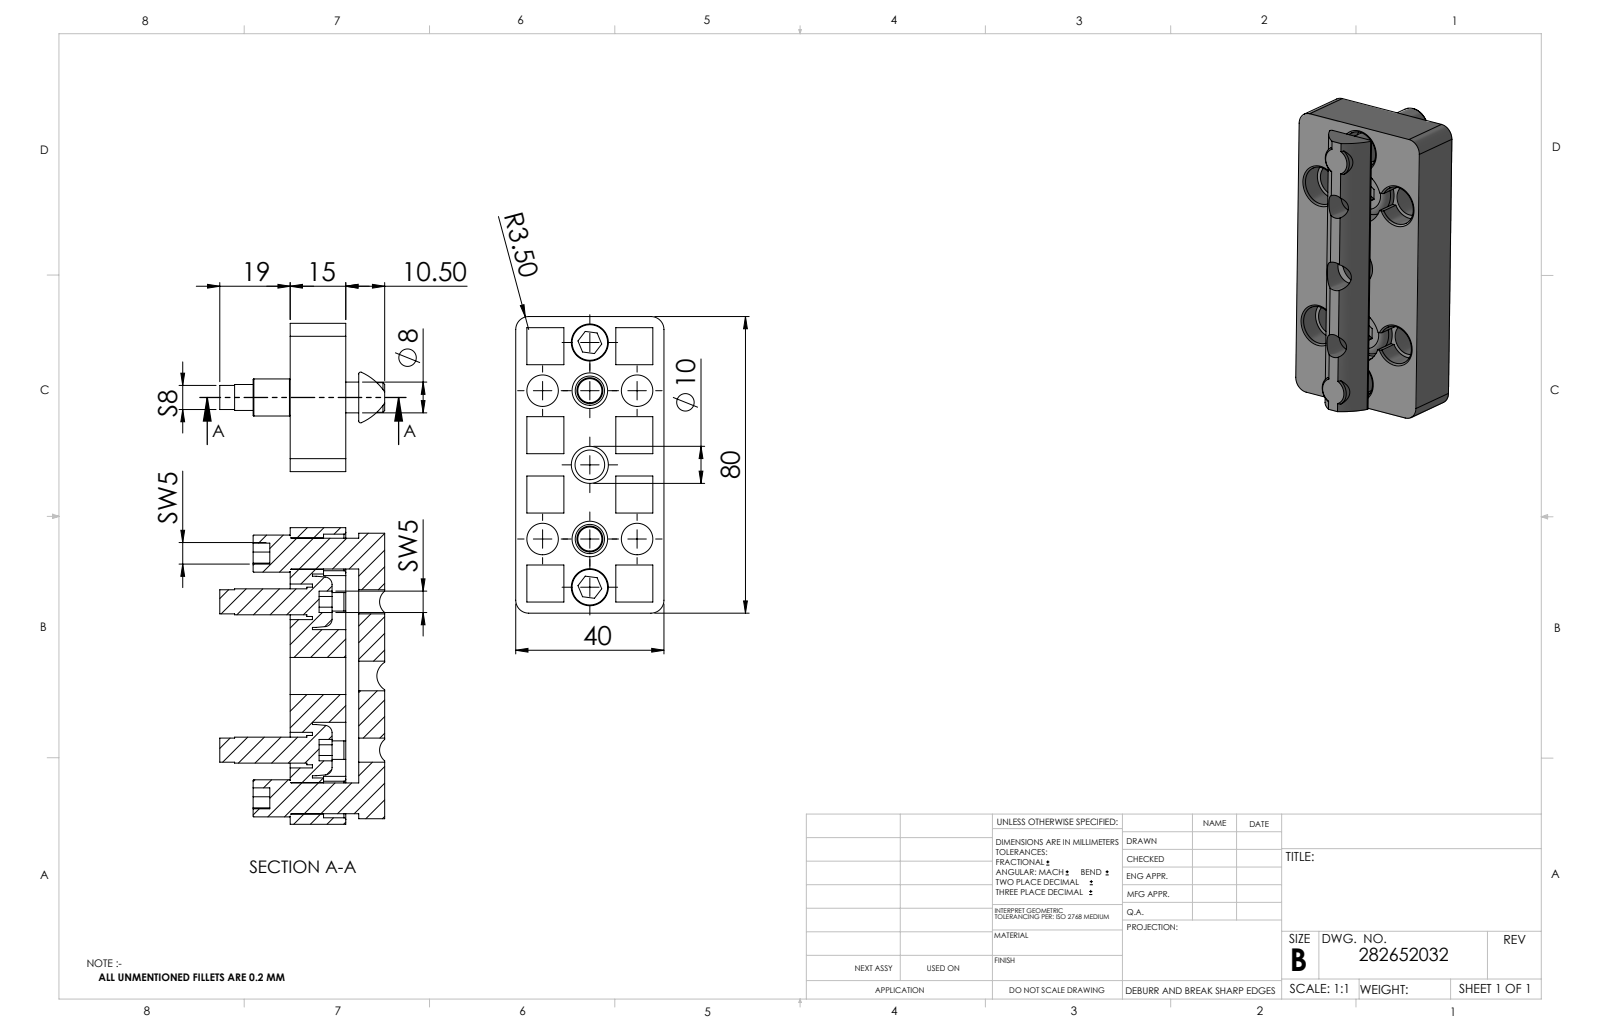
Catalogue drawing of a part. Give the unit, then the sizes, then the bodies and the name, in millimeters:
Units: millimetres
Overall size (bounding box): 80 × 44.5 × 40
Round holes (diameter × count): ⌀8.5 ×6, ⌀10.5 ×6, ⌀6.5 ×2, ⌀9.6 ×2, ⌀15 ×2, ⌀8 ×1, ⌀10 ×1
Round bosses / shafts (diameter × count): ⌀13.8 ×2, ⌀10 ×2, ⌀8.3 ×2, ⌀7.9 ×2, ⌀7 ×2
Partial cylindrical surfaces — rounded edges, fillets, slot ends (radius × count): R3.5 ×4, R0.5 ×2, R4 ×2, R15 ×2
Main face-to-face distances: 9.99, 15, 3, 12.99, 40, 24, 40.01, 27.01, 37, 24.01
Hole centre spacings: 12.75, 18.21, 23.72, 41.98, 54.51, 40, 13, 20
Volume: 37 025 mm³ · Surface area: 23 512 mm²
Bodies: 1 solid, 228 faces (113 planar, 79 cylindrical, 36 other)
Part name (STEP PRODUCT): 282652032_c_1
STEP written by: SolidWorks 2014 (CONFIG_CONTROL_DESIGN)
